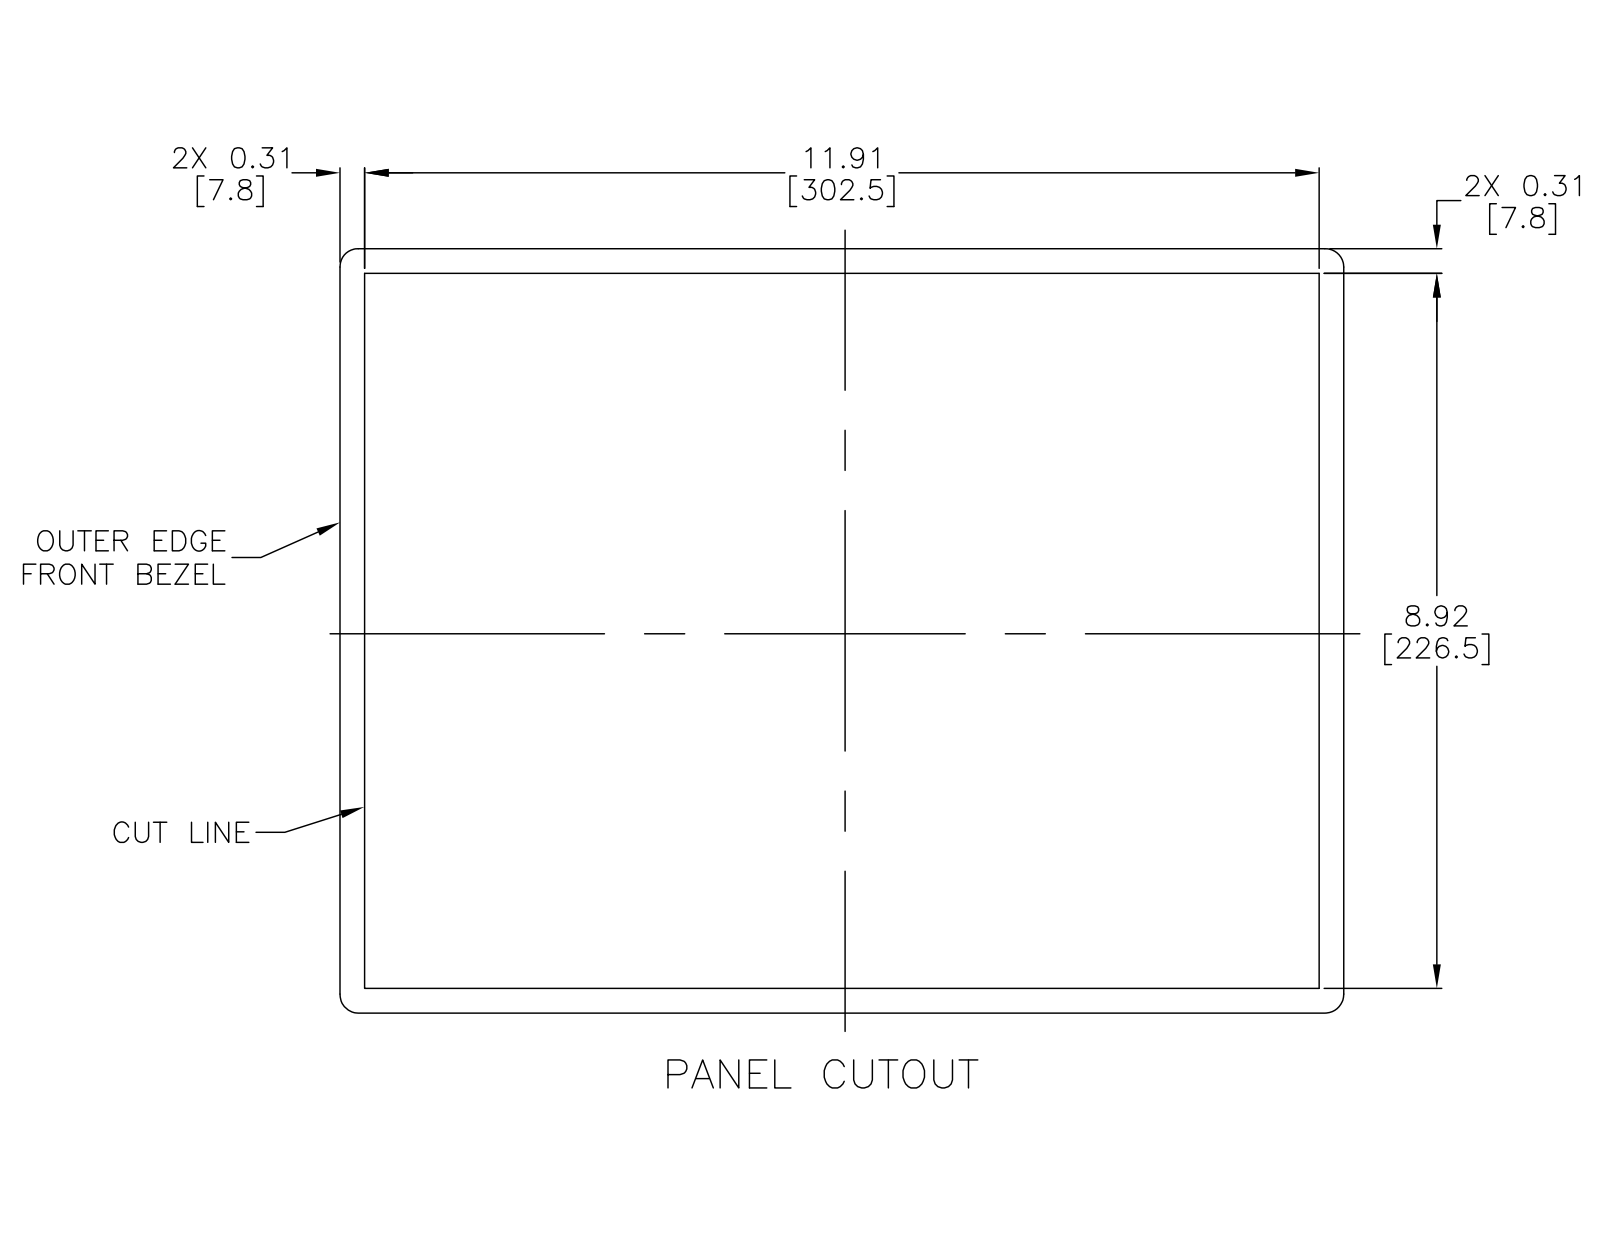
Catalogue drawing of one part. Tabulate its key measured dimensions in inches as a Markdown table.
| quantity | value |
| --- | --- |
| part name | EA9-T10CL |
| STEP written by | SolidWorks 2014 (AUTOMOTIVE_DESIGN) |
| units | inches |
| bodies | 9 solids, 2148 faces (1138 planar, 951 cylindrical, 59 other) |
| overall size | 12.52 × 9.53 × 2.408 |
| volume | 41.24 in³ |
| surface area | 756.7 in² |
| round holes (diameter × count) | 0.045 × 14, 0.07 × 2, 0.08 × 2, 0.1 × 2, 0.14 × 2, 0.4 × 2, 0.045 × 1 |
| round bosses / shafts (diameter × count) | 0.05 × 5, 0.25 × 2 |
| partial cylindrical surfaces (radius × count) | 0.04 × 203, 0.045 × 167, 0.031 × 77, 0.038 × 52, 0.125 × 26, 0.041 × 20, 0.063 × 10, 0.123 × 9 |
| main face-to-face distances | 0.06, 2.189, 0.06, 0.37, 1.819, 2.249, 2.129, 1.73, 2.16, 2.1 |
| hole center spacings | 0.115, 0.229, 0.148, 0.219, 0.343, 0.15, 0.229, 0.458 |
